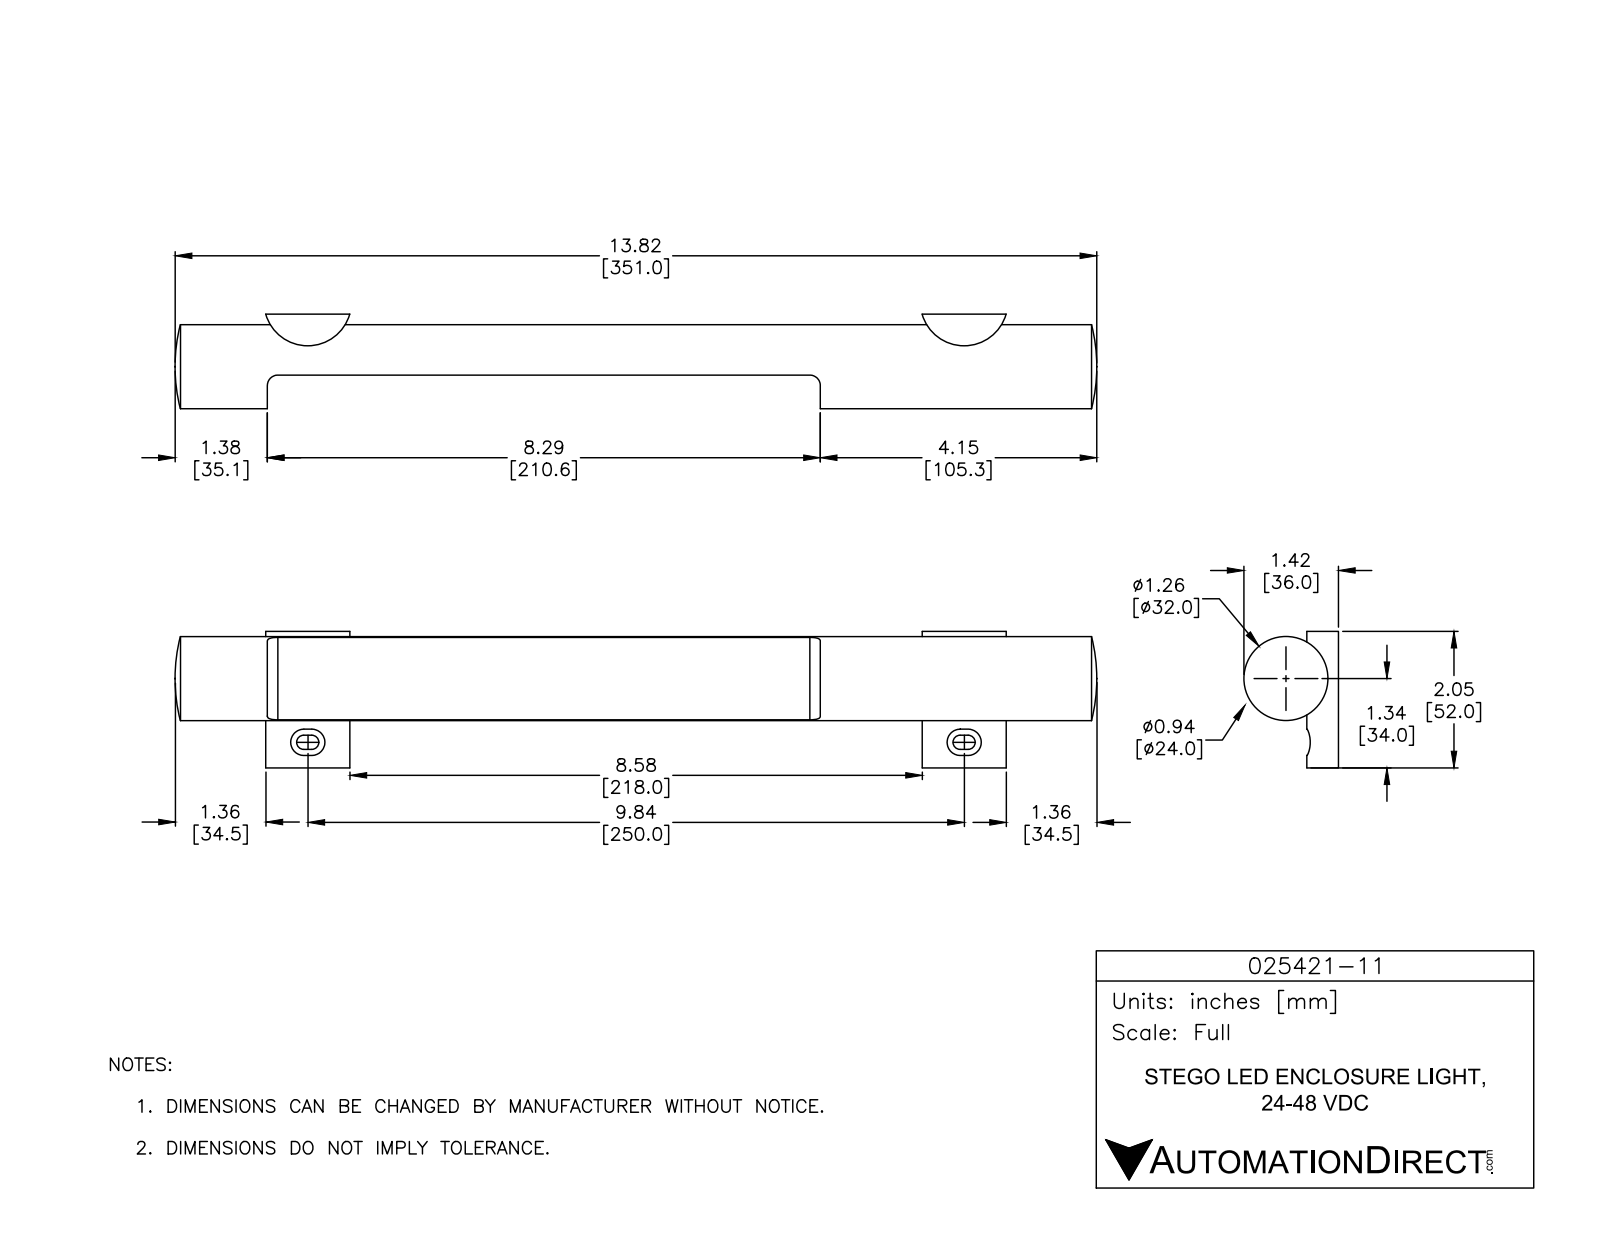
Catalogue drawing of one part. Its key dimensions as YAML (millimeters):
part_name: "PRODUCT_NAME_1"
step_written_by: "ACIS (CONFIG_CONTROL_DESIGN)"
units: millimeters
bodies: {solids: 1, faces: 37, planar: 19, cylindrical: 14, other: 4}
overall_size: [351, 52, 36]
volume: 239165
surface_area: 40885
round_bosses_or_shafts:
  - {diameter: 32, count: 1}
partial_cylinders:
  - {radius: 2.7, count: 4}
  - {radius: 5, count: 4}
  - {radius: 4, count: 2}
  - {radius: 16.64, count: 2}
face_to_face_distances: [23.2, 52, 210.6, 2, 21.2, 4.75, 14.75, 10, 47.25, 37.25]
